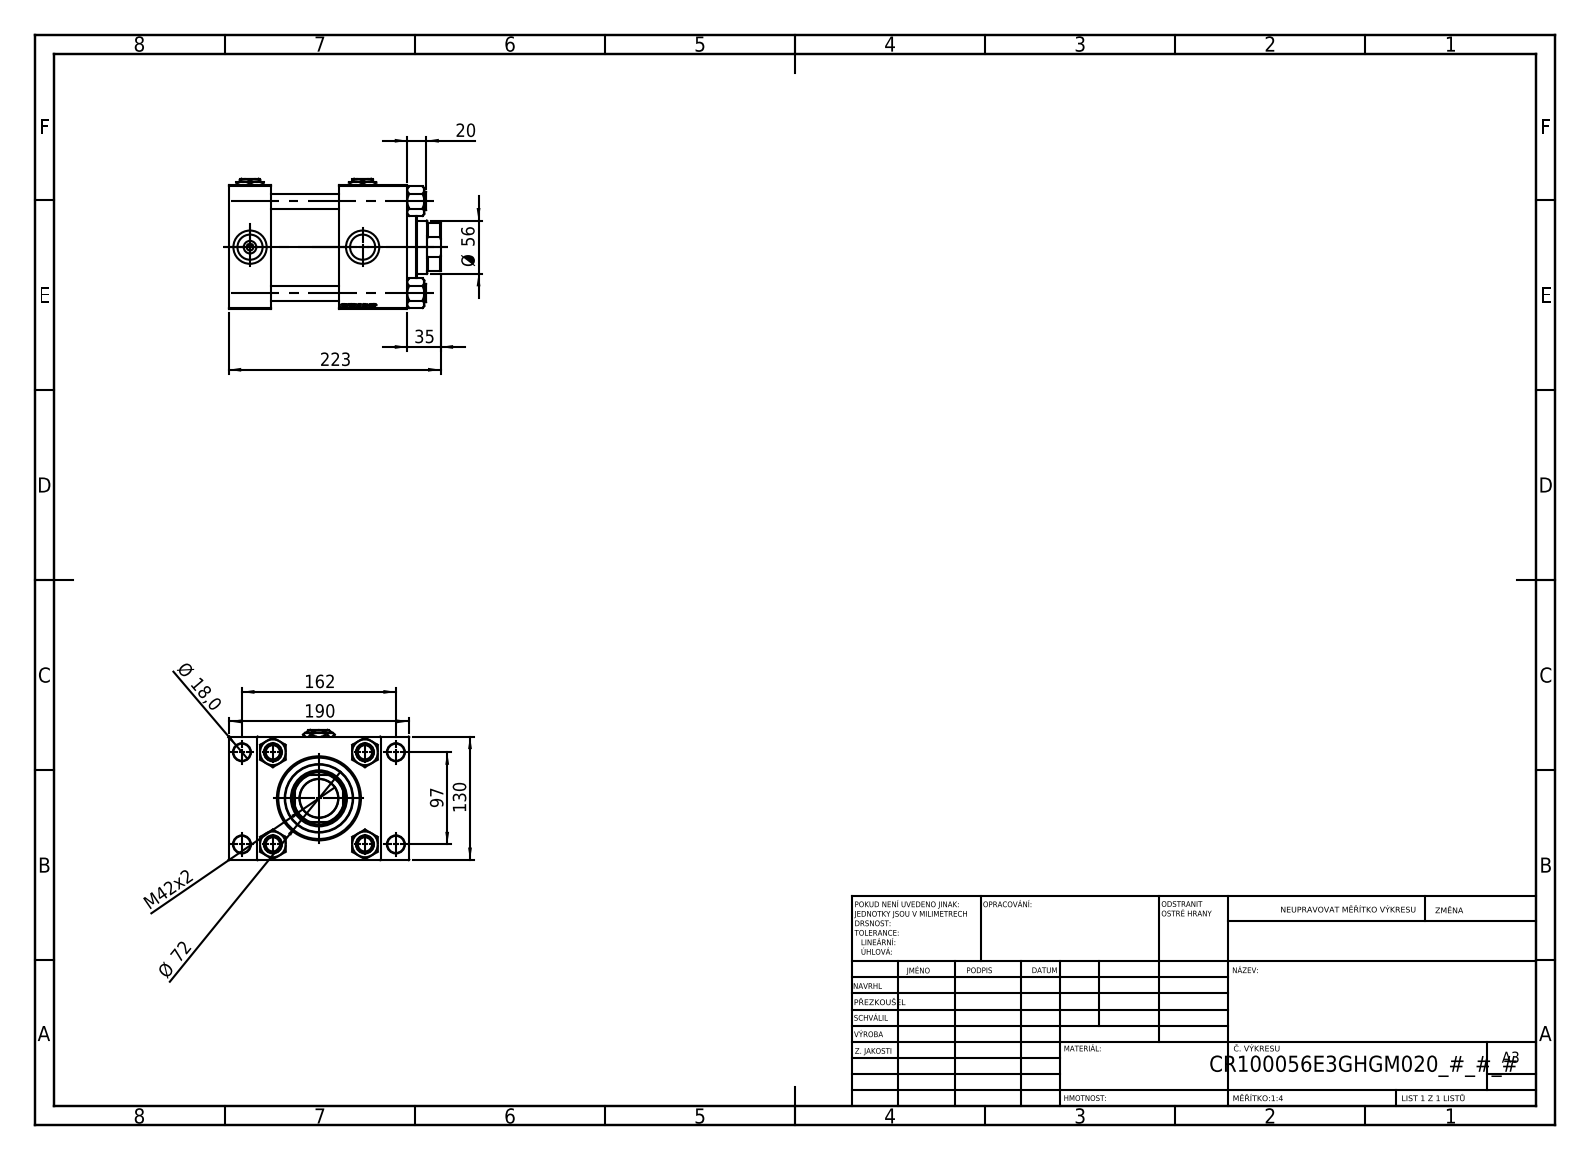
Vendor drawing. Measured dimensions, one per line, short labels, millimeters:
name: V215_VC_A; V215CR_VCP_E; V215CR_E_Body; V215CR_TYCINKA_E (+2 more)
written by: SolidWorks 2019 (CONFIG_CONTROL_DESIGN)
unit: mm
bodies: 13 solids, 1284 faces (593 planar, 97 cylindrical, 594 other)
size: 223 × 190 × 137
volume: 2 780 000 mm³; area: 384 309 mm²
holes: 4× ⌀16, 4× ⌀18, 4× ⌀26.44, 4× ⌀35, 3× ⌀7, 1× ⌀40.5, 1× ⌀56, 1× ⌀59, 1× ⌀76, 1× ⌀85.5, 1× ⌀100
bosses: 4× ⌀19, 1× ⌀106, 1× ⌀72
rounds: 1× R27
face distances: 130, 45, 188, 143, 30, 160, 71, 116, 72, 20
hole spacings: 32.55, 68.52, 94.41, 96.9, 102.27, 129.45, 161.73, 97
